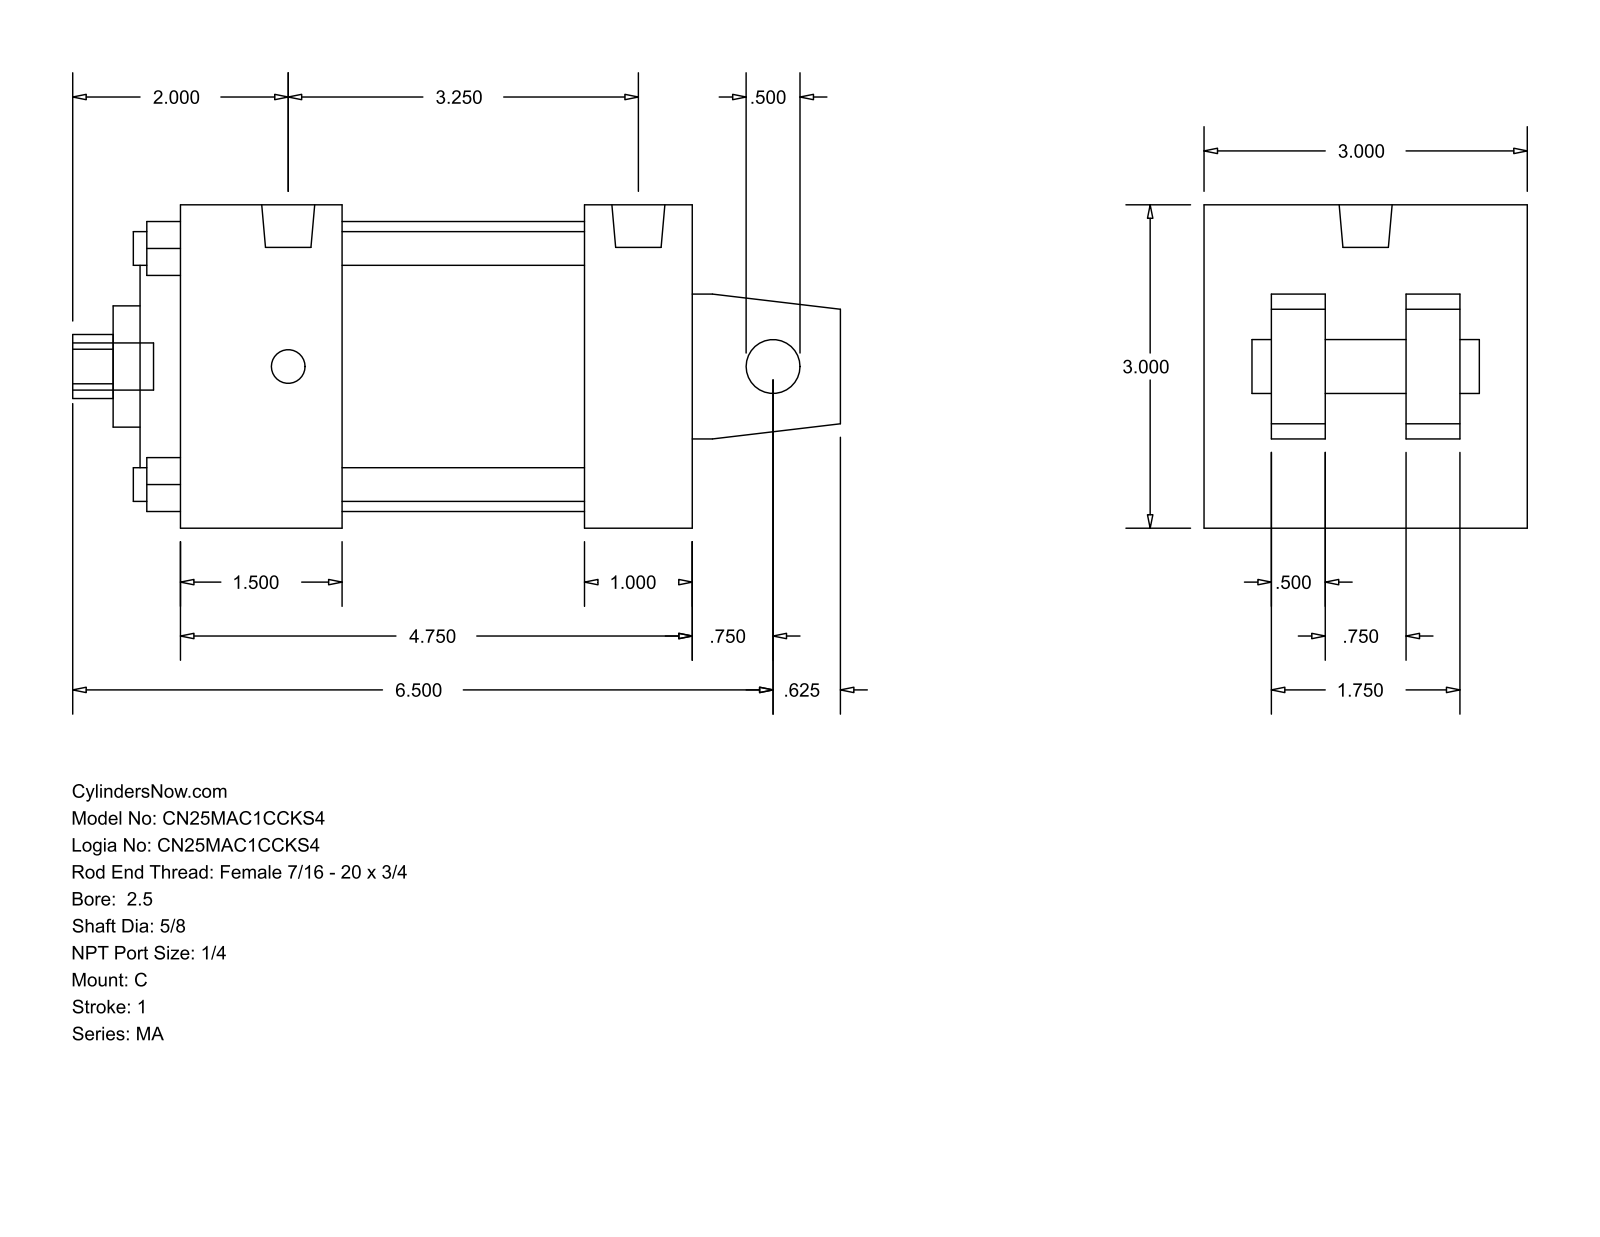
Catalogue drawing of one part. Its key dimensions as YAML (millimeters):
part_name: "MA_C__0250_0.625"
step_written_by: "GSSL Pune (CONFIG_CONTROL_DESIGN)"
units: millimeters
bodies: {solids: 0, faces: 105, planar: 77, cylindrical: 28, other: 0}
overall_size: [180.97, 76.2, 76.2]
round_holes:
  - {diameter: 7.94, count: 4}
  - {diameter: 12.7, count: 1}
  - {diameter: 15.88, count: 1}
  - {diameter: 28.57, count: 1}
  - {diameter: 50.8, count: 1}
  - {diameter: 68.33, count: 1}
round_bosses_or_shafts:
  - {diameter: 7.94, count: 4}
  - {diameter: 12.49, count: 2}
  - {diameter: 11.11, count: 1}
partial_cylinders:
  - {radius: 7.54, count: 1}
face_to_face_distances: [76.2, 120.65, 12.7, 15.87, 47.63, 25.4, 57.15, 38.1, 95.25, 82.55]
hole_center_spacings: [39.33, 55.62, 78.66]
